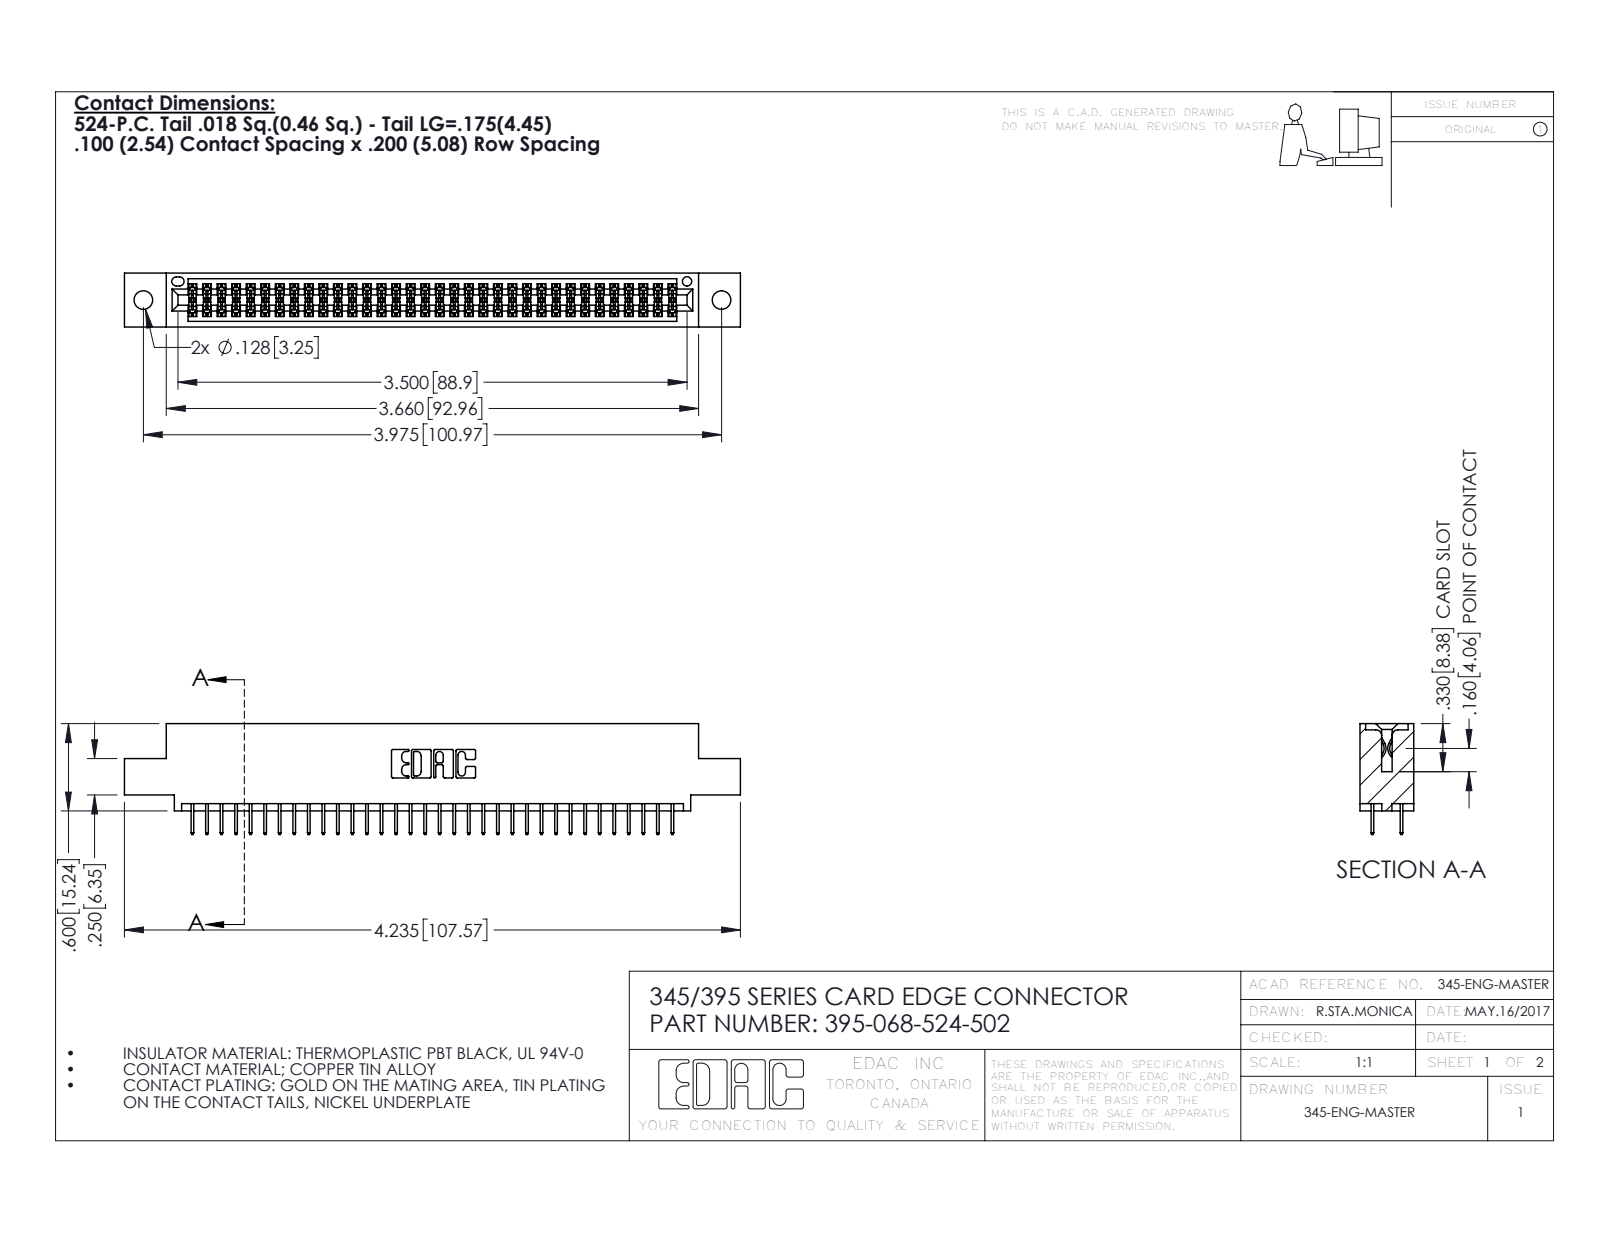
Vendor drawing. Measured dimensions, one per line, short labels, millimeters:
name: 345-292-001_345-293-124; 345 Part_0.110 Offset - 0.128 Dia; 395-068-524-502
written by: SolidWorks 2016 (CONFIG_CONTROL_DESIGN)
unit: mm
bodies: 69 solids, 3802 faces (2736 planar, 1066 cylindrical, 0 other)
size: 107.6 × 19.4 × 9.4
volume: 10 200 mm³; area: 14 410 mm²
holes: 2× ⌀3.3, 1× ⌀1.6
rounds: 102× R0.2, 22× R0.3, 6× R0.2, 6× R0.8, 3× R0.7, 2× R0.4, 2× R0.5, 2× R0.6
face distances: 1.8, 7.6, 5.1, 9.4, 2.5, 6.9, 0.6, 5.7, 1.8, 4.4
hole spacings: 6.9, 95, 101
